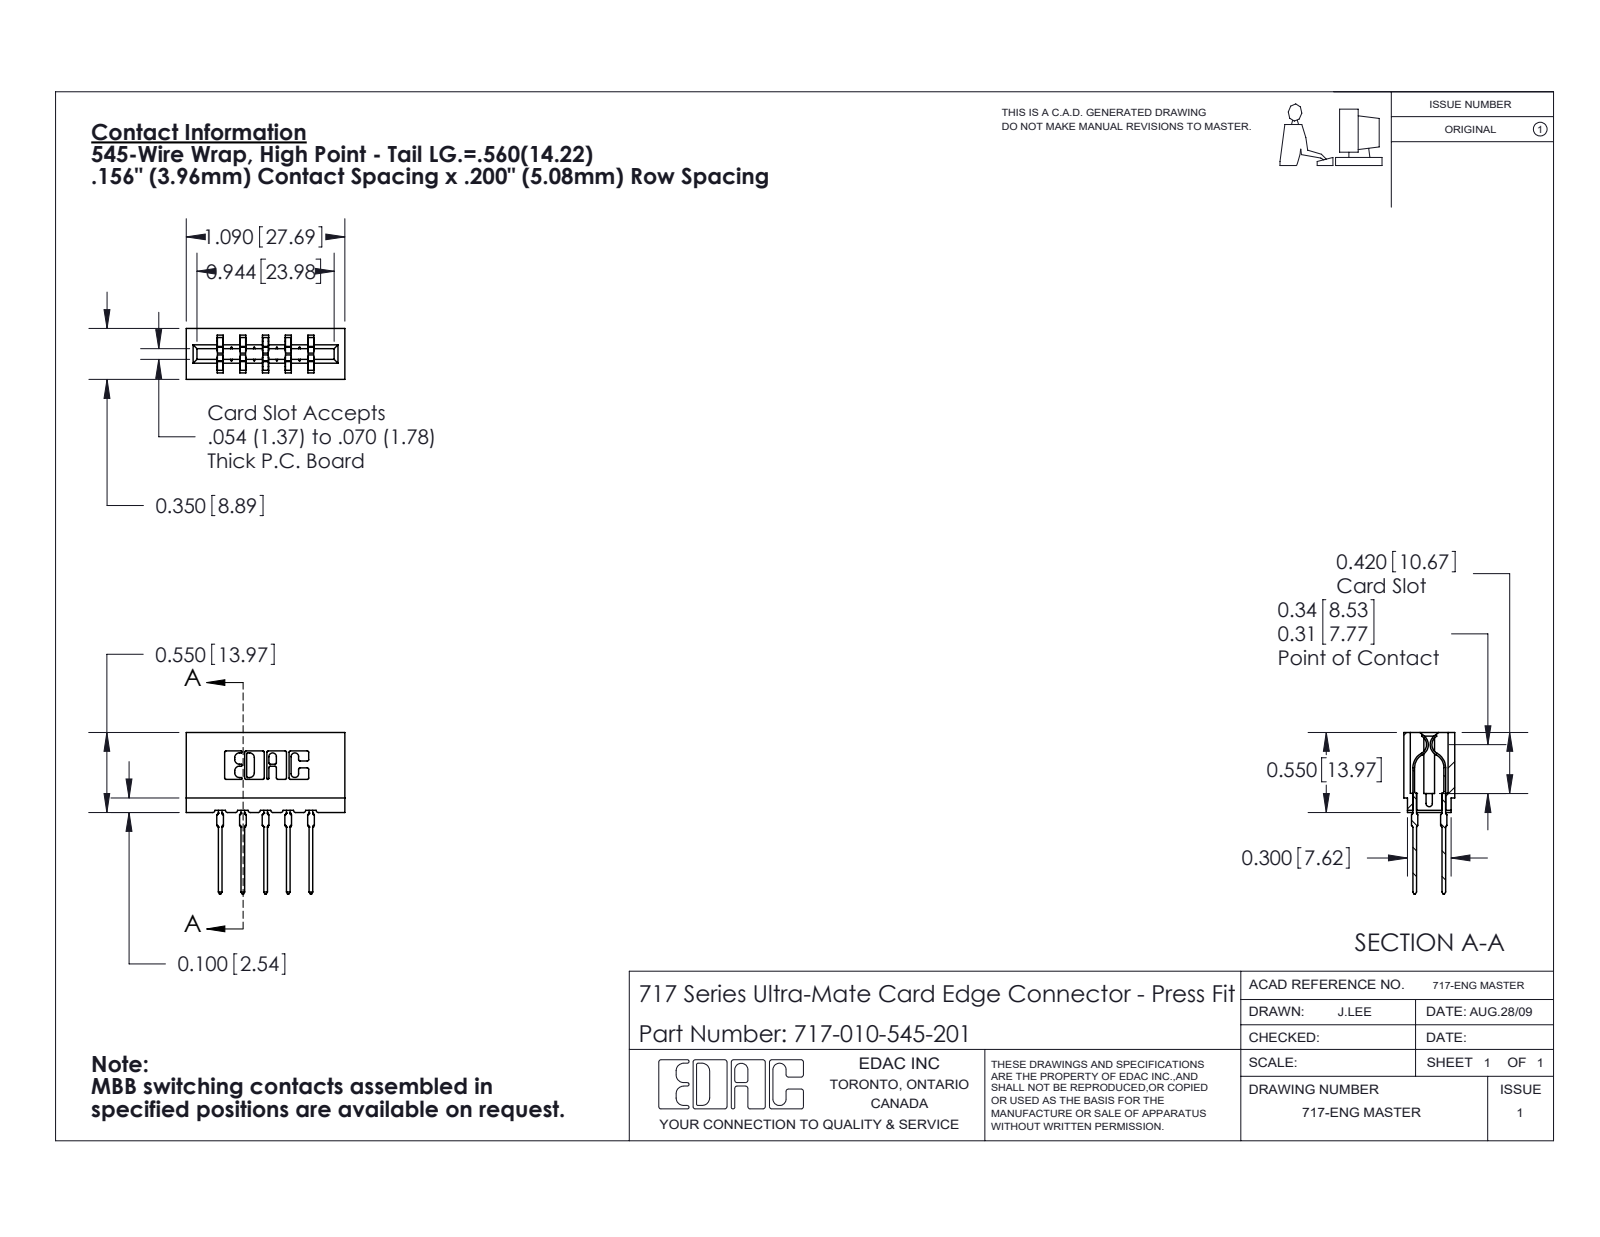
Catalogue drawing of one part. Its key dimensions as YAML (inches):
part_name: "745-292-001_545; 717 Part_Insulator Option - 06; 717-010-545-201"
step_written_by: "SolidWorks 2020 (CONFIG_CONTROL_DESIGN)"
units: inches
bodies: {solids: 11, faces: 994, planar: 519, cylindrical: 215, other: 260}
overall_size: [1.109, 1.09, 0.35]
volume: 0.158
surface_area: 5.627
partial_cylinders:
  - {radius: 0.01, count: 22}
  - {radius: 0.021, count: 20}
  - {radius: 0.015, count: 10}
  - {radius: 0.005, count: 8}
  - {radius: 0.011, count: 8}
  - {radius: 0.007, count: 6}
  - {radius: 0.031, count: 6}
  - {radius: 0.026, count: 3}
face_to_face_distances: [0.212, 0.156, 0.138, 0.35, 0.198, 0.042, 0.063, 0.287, 0.076, 0.149]
